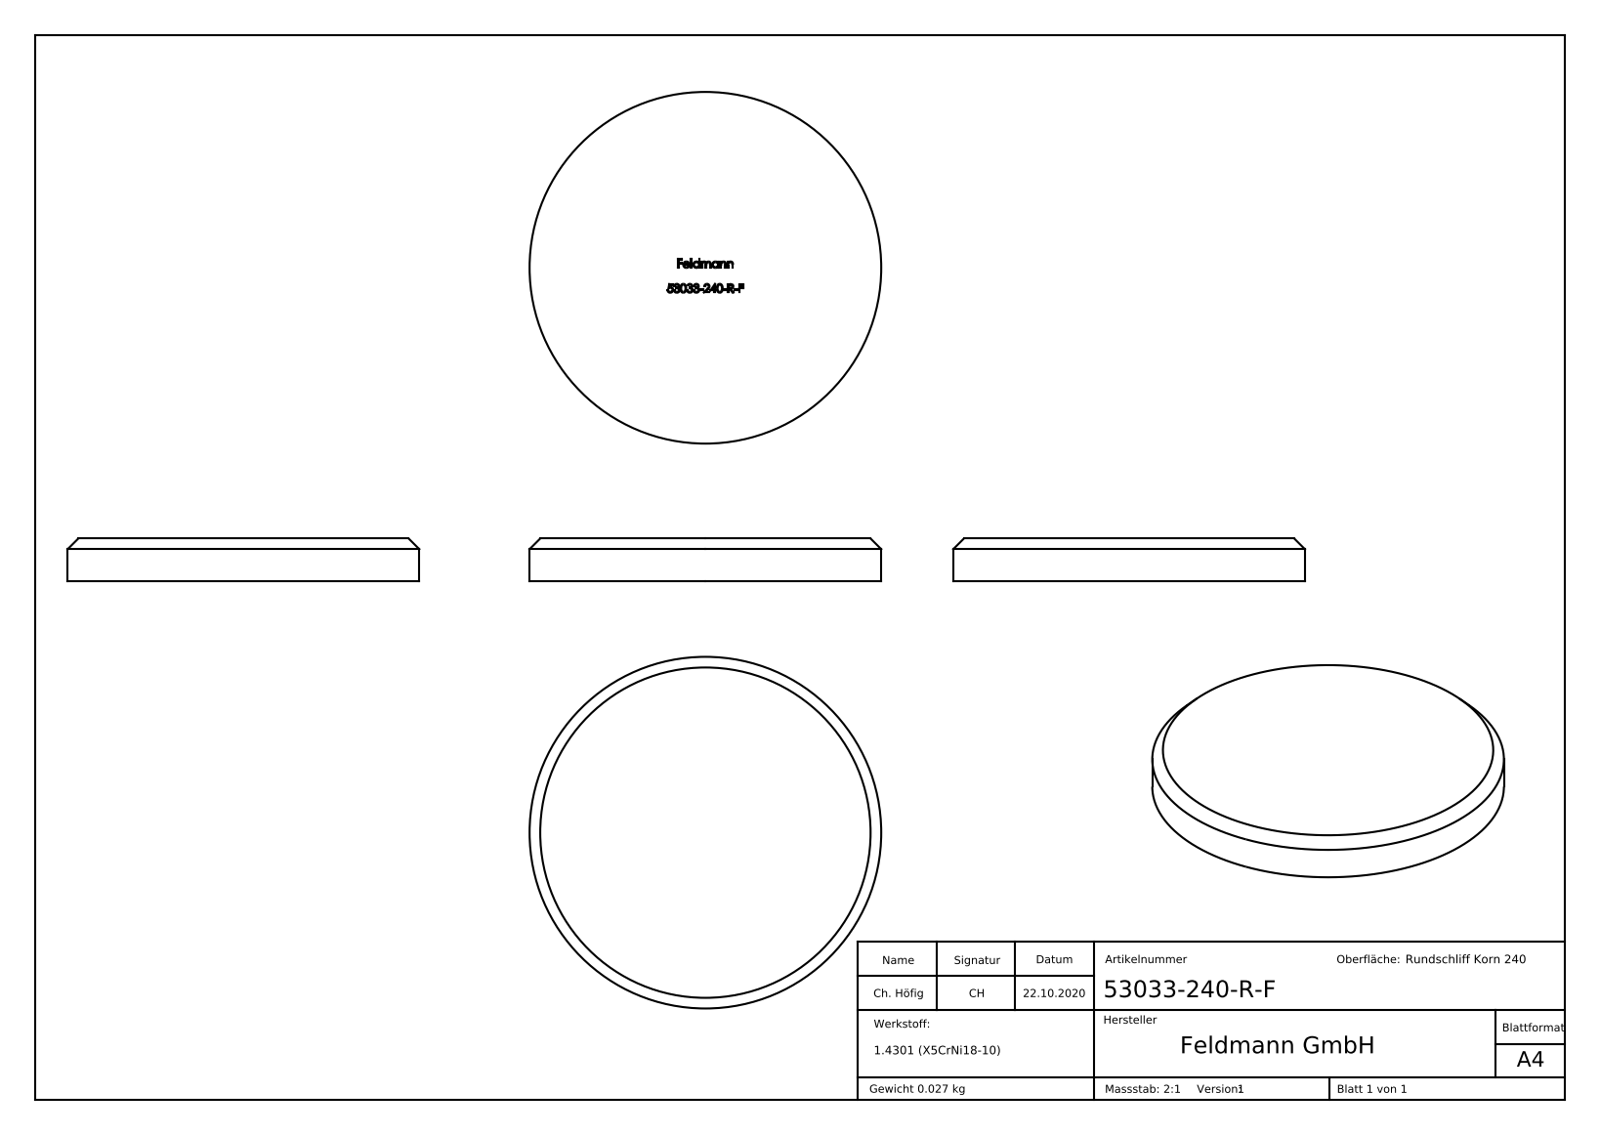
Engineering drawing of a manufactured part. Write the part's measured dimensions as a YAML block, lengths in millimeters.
part_name: "53033-240-R-F"
step_written_by: "SolidWorks 2018 (CONFIG_CONTROL_DESIGN)"
units: millimeters
bodies: {solids: 1, faces: 282, planar: 151, cylindrical: 2, other: 129}
overall_size: [33, 33, 4]
volume: 3370
surface_area: 2070
round_bosses_or_shafts:
  - {diameter: 33, count: 1}
face_to_face_distances: [4, 3.9, 2.32, 1.21, 3.49, 0.79, 1.78, 2.2, 2.24, 0.83]
